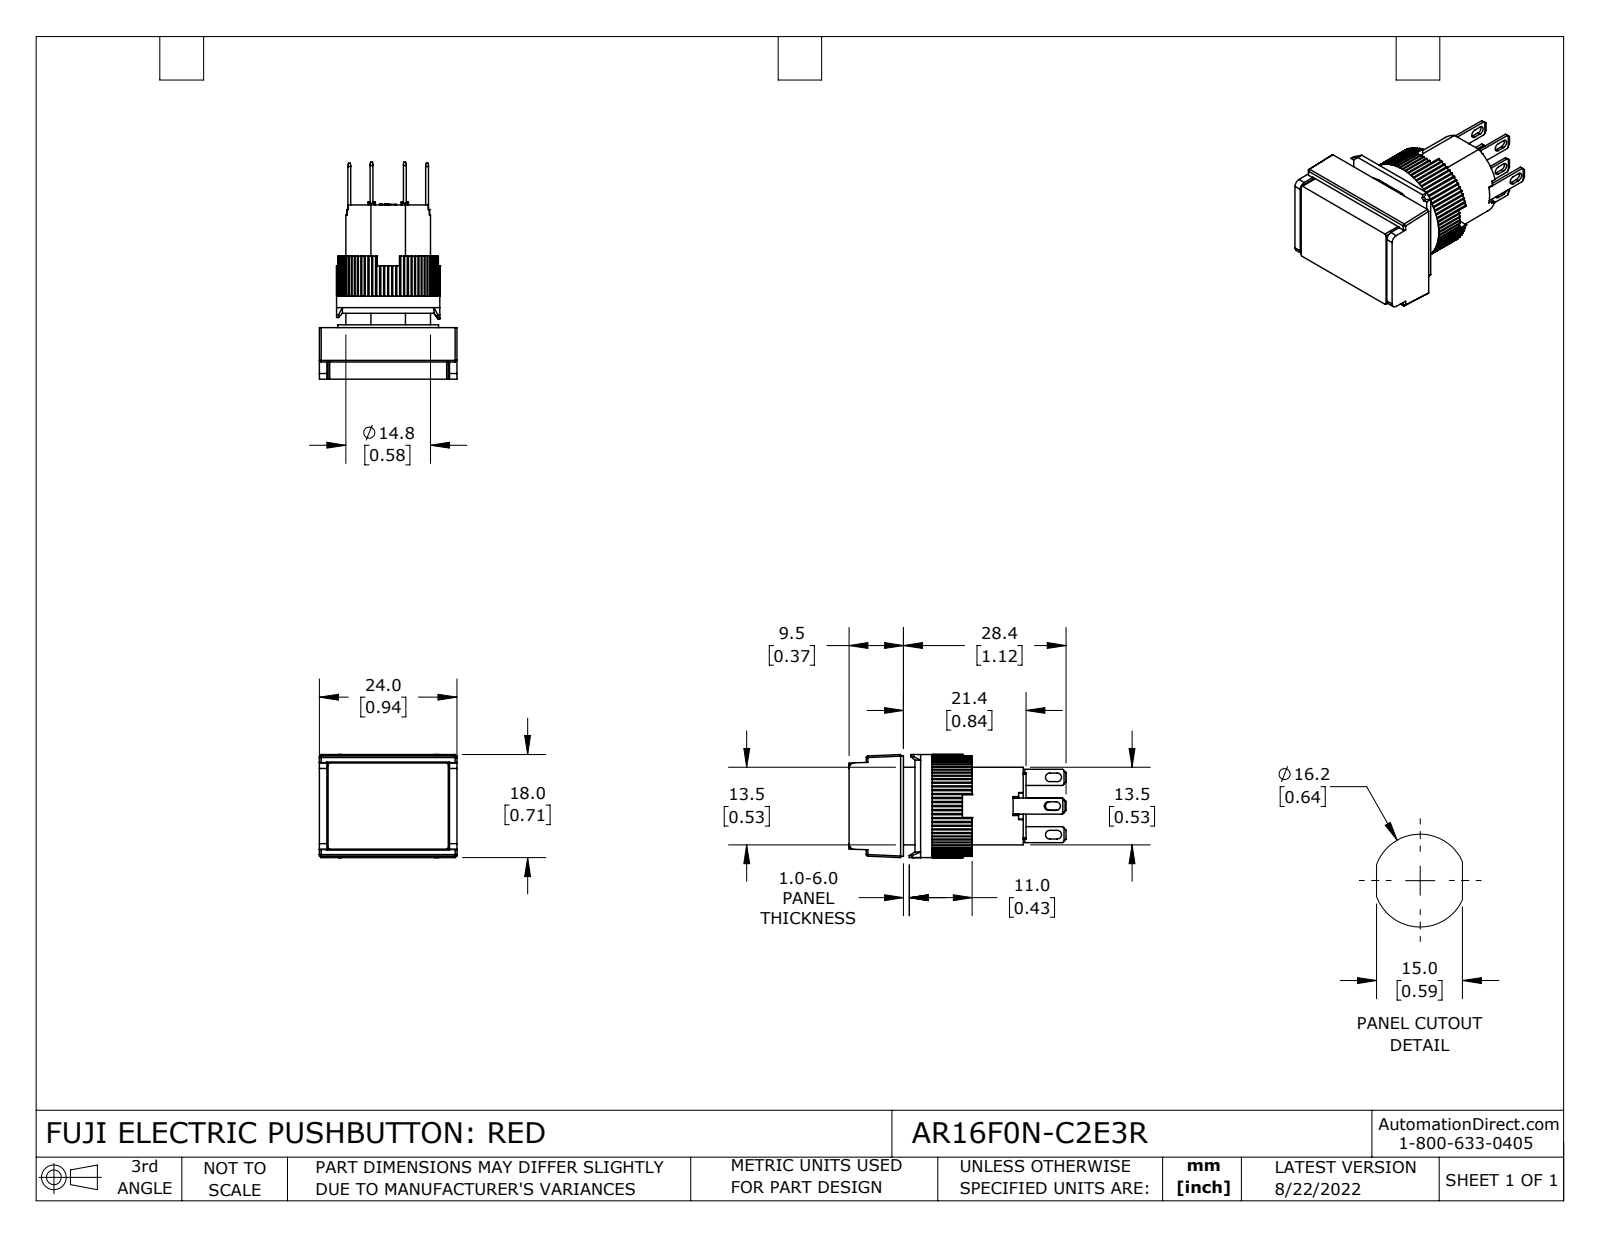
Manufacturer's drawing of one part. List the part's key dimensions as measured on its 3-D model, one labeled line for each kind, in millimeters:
Part name (STEP PRODUCT): AR16F0N-C2E3R
STEP written by: SolidWorks 2021 (CONFIG_CONTROL_DESIGN)
Units: millimetres
Bodies: 14 solids, 843 faces (656 planar, 183 cylindrical, 4 other)
Overall size (bounding box): 37.9 × 24 × 18
Volume: 7 280 mm³ · Surface area: 6 004 mm²
Round holes (diameter × count): ⌀13.8 ×1, ⌀14.8 ×1
Round bosses / shafts (diameter × count): ⌀18 ×1, ⌀17.6 ×1
Partial cylindrical surfaces — rounded edges, fillets, slot ends (radius × count): R0.3 ×80, R0.2 ×12, R0.8 ×8, R0.3 ×6, R1 ×2
Main face-to-face distances: 5.4, 9, 3.6, 8.9, 12.5, 3.5, 0.5, 21.4, 1.5, 11.5
